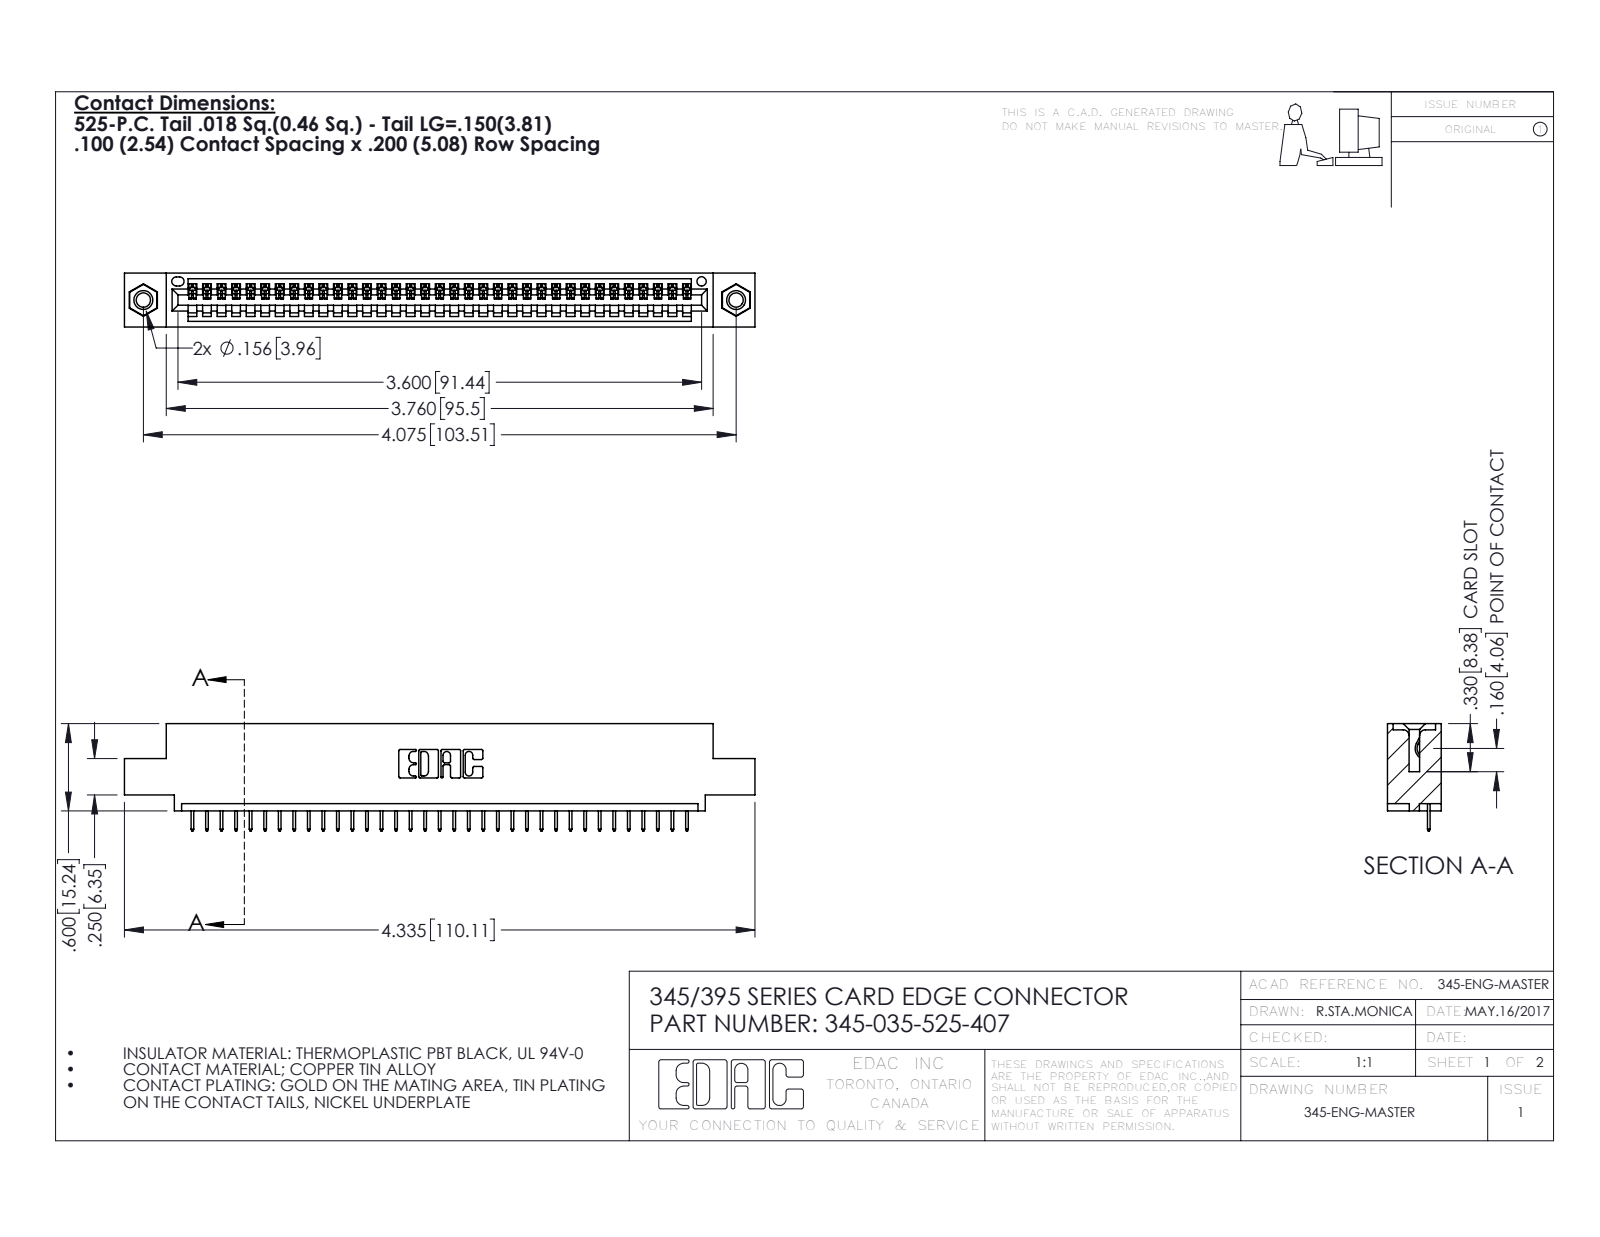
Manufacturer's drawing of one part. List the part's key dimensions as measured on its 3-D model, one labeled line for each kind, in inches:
Part name (STEP PRODUCT): 345 Part_0.110 Offset - 0.156 Dia-TI; 345-250-001_345-250-005-103; 345-292-001_345-293-125; 345-035-525-407
STEP written by: SolidWorks 2020 (CONFIG_CONTROL_DESIGN)
Units: inches
Bodies: 38 solids, 2360 faces (1726 planar, 618 cylindrical, 16 other)
Overall size (bounding box): 4.335 × 0.737 × 0.37
Volume: 0.621 in³ · Surface area: 20.24 in²
Round holes (diameter × count): ⌀0.098 ×2, ⌀0.125 ×2, ⌀0.156 ×2, ⌀0.064 ×1
Round bosses / shafts (diameter × count): ⌀0.155 ×2
Partial cylindrical surfaces — rounded edges, fillets, slot ends (radius × count): R0.006 ×70, R0.01 ×22, R0.007 ×6, R0.031 ×6, R0.026 ×3, R0.031 ×2, R0.04 ×2, R0.014 ×1
Main face-to-face distances: 0.072, 0.298, 0.37, 0.2, 0.098, 0.272, 0.025, 0.225, 0.072, 0.149
Hole centre spacings: 0.27, 3.839, 4.075
